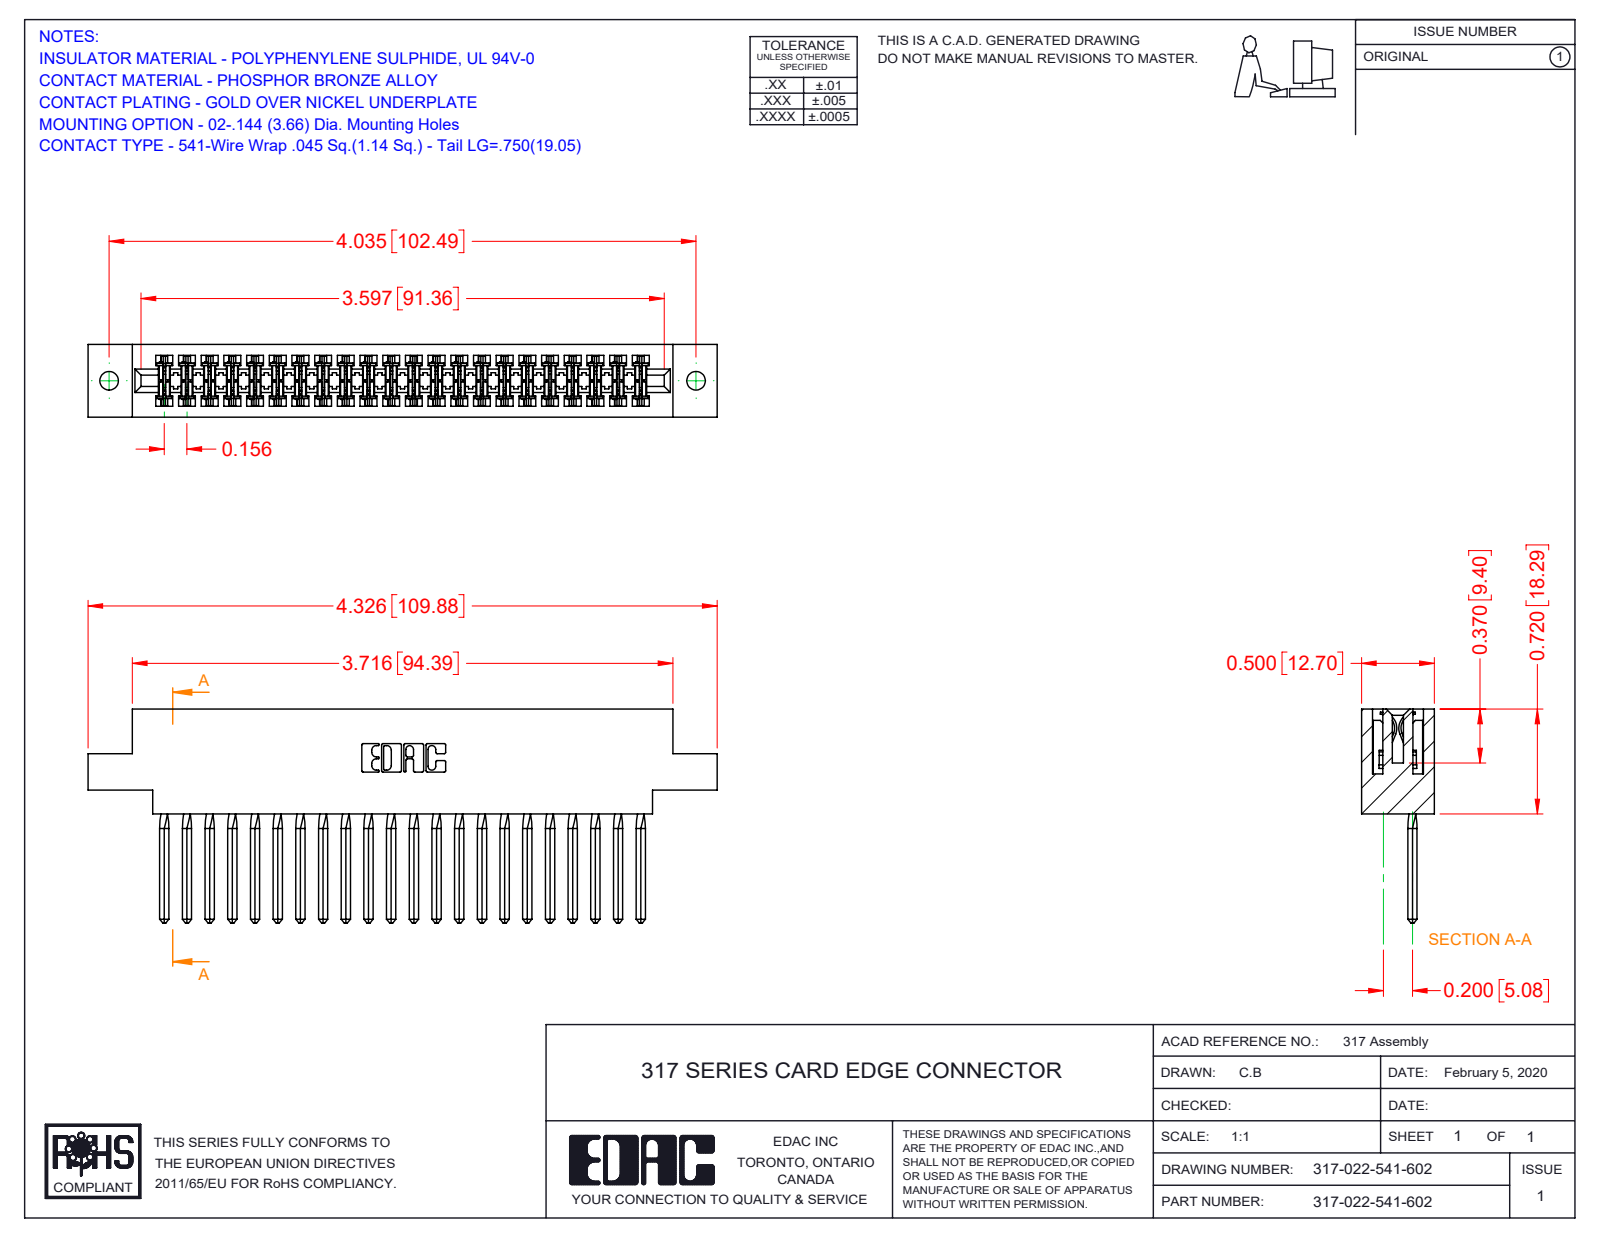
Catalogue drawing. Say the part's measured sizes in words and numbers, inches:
The part is named "317-022-541-602; 317-290-002_541; 317 Part_.144 Dia". Its 3-D file was written by "SolidWorks 2016 (CONFIG_CONTROL_DESIGN)". It is 23 solids with 3446 faces: 2786 planar, 572 cylindrical and 88 other. Overall it measures 4.326 by 1.47 by 0.5 inches. Its volume is 1.048 cubic inches and its surface area 36.15 square inches. Round holes: 2 of diameter 0.128. Partial cylindrical surfaces (rounded edges, fillets, slot ends): 44 of radius 0.015, 22 of radius 0.01, 6 of radius 0.007, 6 of radius 0.031, 3 of radius 0.026, 2 of radius 0.095, 2 of radius 0.1, 2 of radius 0.11. The main face-to-face distances are 0.5, 0.075, 0.425, 0.11, 0.35, 0.195, 0.772, 0.22, 0.662, 0.72. The hole center spacings are 4.035.
